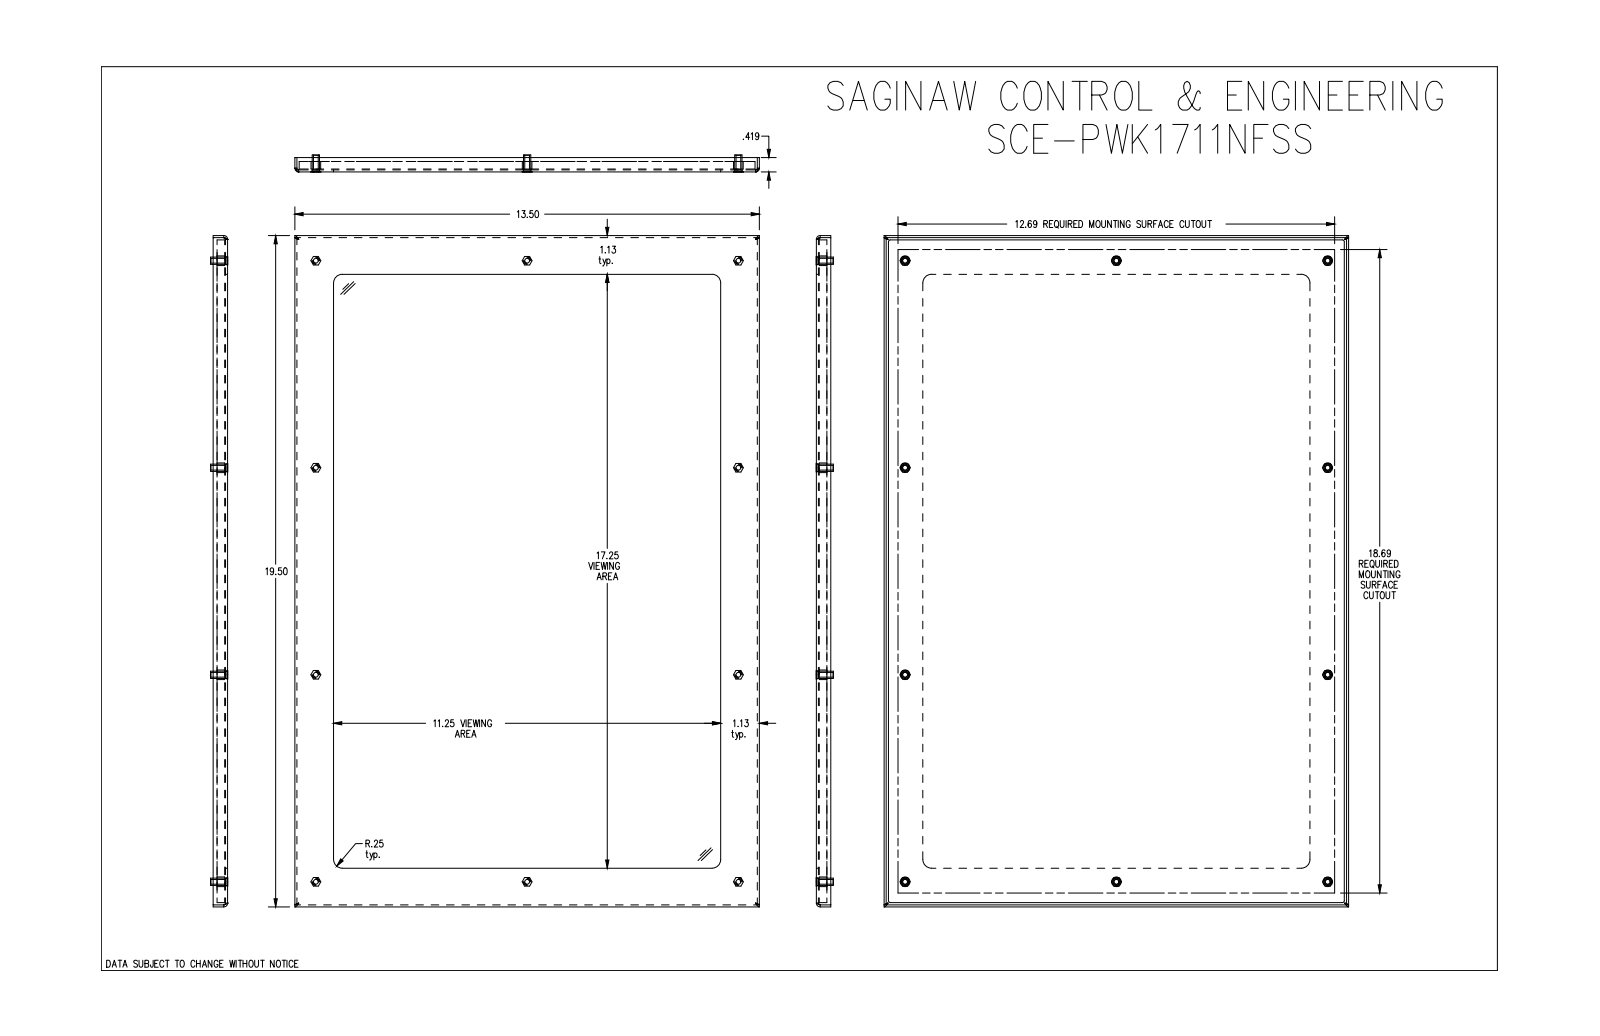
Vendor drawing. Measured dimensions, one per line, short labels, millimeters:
name: SCE-PWK1711NF
written by: SolidWorks 2021 (AUTOMOTIVE_DESIGN)
unit: mm
bodies: 12 solids, 223 faces (121 planar, 82 cylindrical, 20 other)
size: 495.3 × 342.9 × 12.7
volume: 1 074 000 mm³; area: 466 200 mm²
holes: 10× ⌀3.5, 10× ⌀5.4, 10× ⌀7.1
bosses: 10× ⌀5.4
rounds: 4× R1.5, 4× R2.8, 4× R6.4
face distances: 6, 1.5, 6.6, 0.6, 8.2, 2.2, 341.4, 1.7, 3.2, 339.7
hole spacings: 311.9, 347.3, 152.7, 152.7, 347.3, 156, 220.4, 220.5
